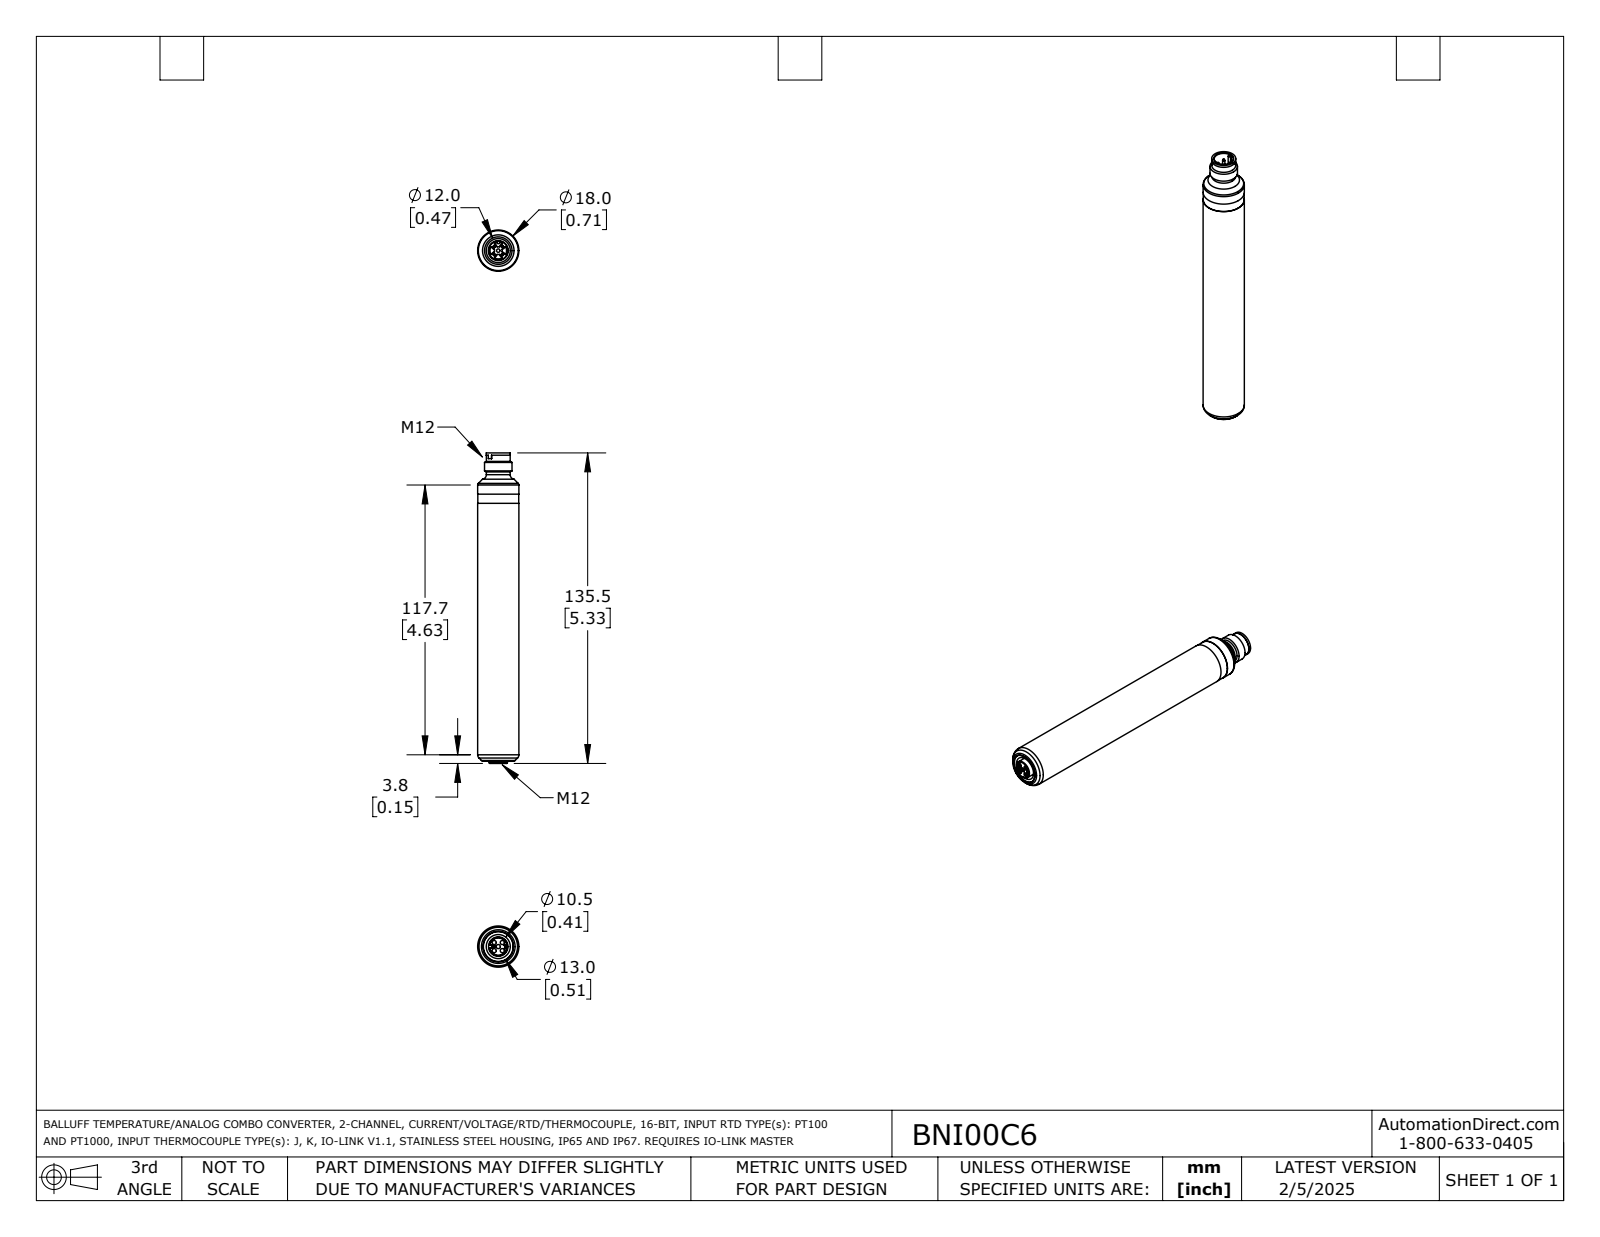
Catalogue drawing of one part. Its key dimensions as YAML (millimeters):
part_name: "BNI00C6"
step_written_by: "SolidWorks 2021 (AUTOMOTIVE_DESIGN)"
units: millimeters
bodies: {solids: 1, faces: 347, planar: 218, cylindrical: 95, other: 34}
overall_size: [135.5, 18, 18]
volume: 31410
surface_area: 8877
round_holes:
  - {diameter: 1.8, count: 5}
  - {diameter: 8.2, count: 1}
  - {diameter: 8.3, count: 1}
  - {diameter: 10.5, count: 1}
  - {diameter: 13, count: 1}
round_bosses_or_shafts:
  - {diameter: 1, count: 4}
  - {diameter: 18, count: 1}
  - {diameter: 17.9, count: 1}
  - {diameter: 12, count: 1}
  - {diameter: 10.4, count: 1}
  - {diameter: 8, count: 1}
partial_cylinders:
  - {radius: 0.2, count: 16}
  - {radius: 1.1, count: 4}
  - {radius: 1.8, count: 2}
  - {radius: 0.6, count: 1}
  - {radius: 0.7, count: 1}
  - {radius: 1.7, count: 1}
  - {radius: 3.6, count: 1}
  - {radius: 3.6, count: 1}
face_to_face_distances: [1.5, 7, 5.5, 125.2, 119.7, 118.2, 8.5, 126.7, 134, 135.5]
hole_center_spacings: [2.5, 3.5, 5]
